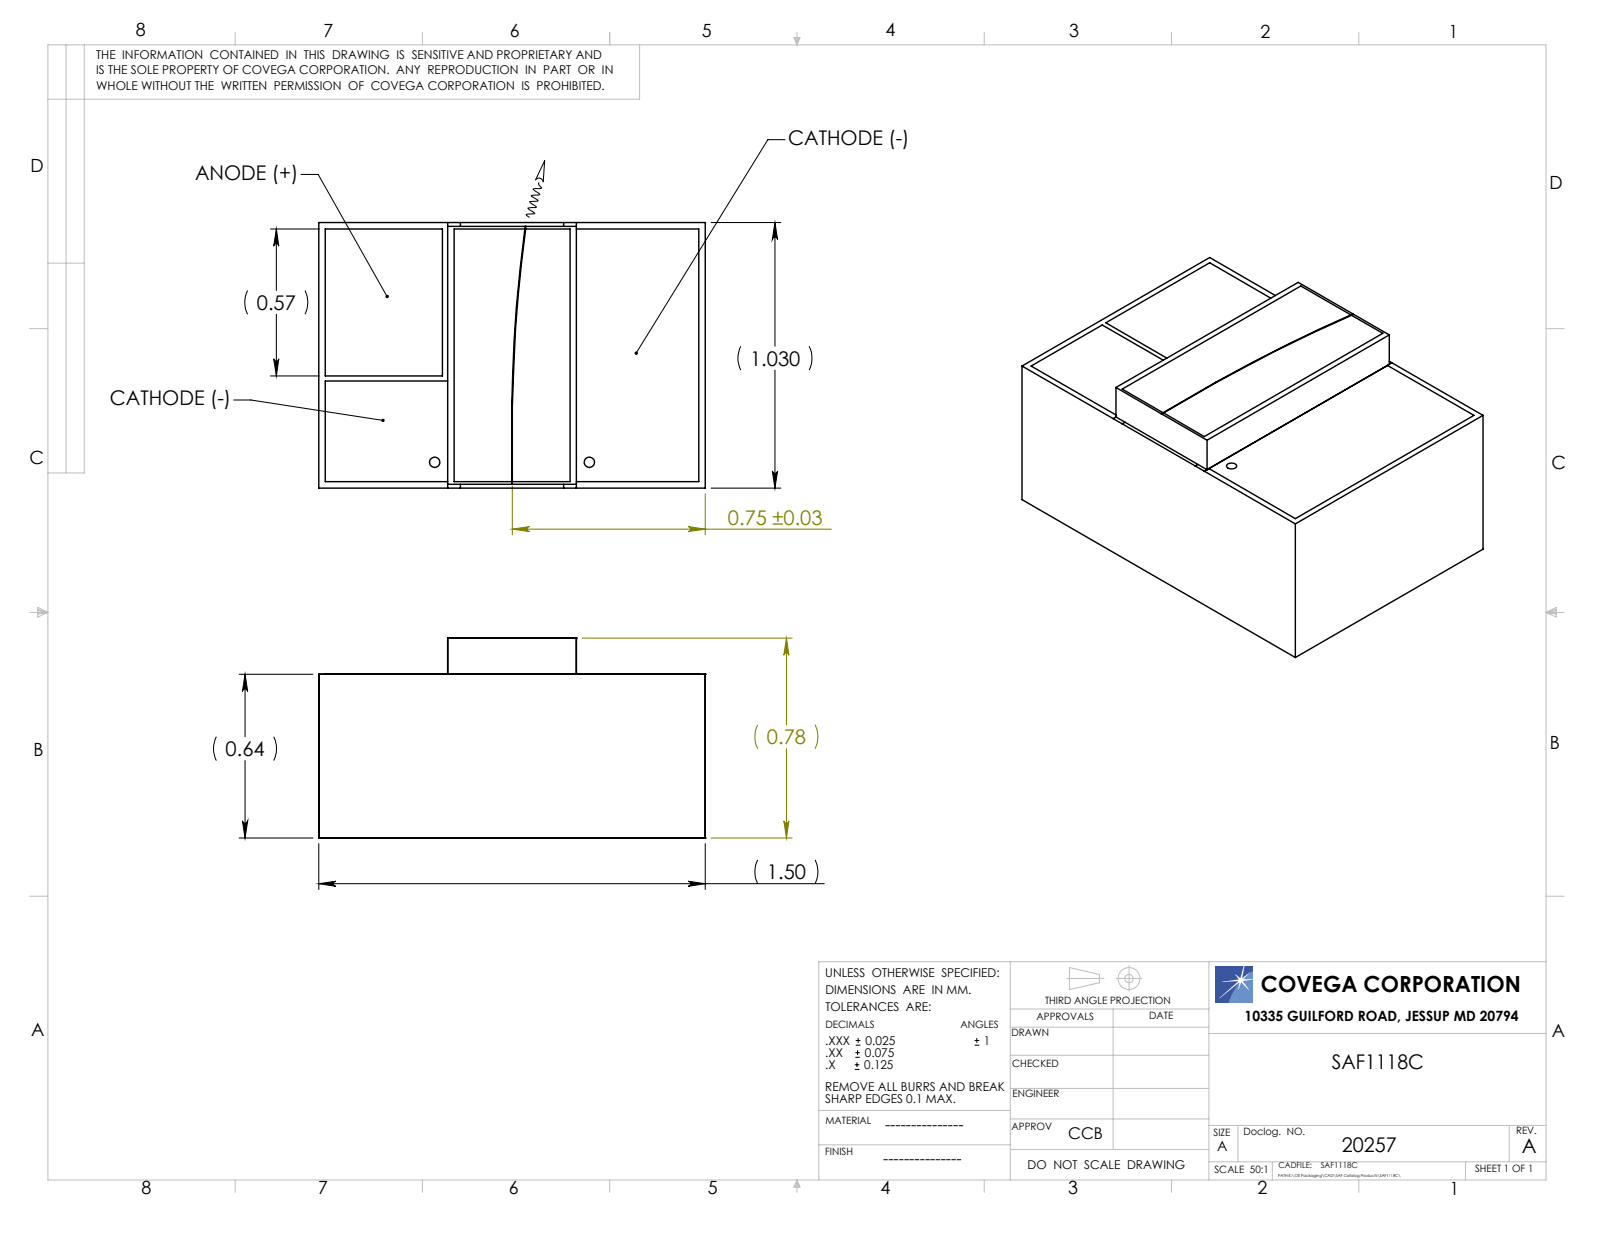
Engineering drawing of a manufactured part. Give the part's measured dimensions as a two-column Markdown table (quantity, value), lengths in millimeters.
| quantity | value |
| --- | --- |
| part name | 20257; 32068-000; 31002-XXX |
| STEP written by | SolidWorks 2009 (AUTOMOTIVE_DESIGN) |
| units | millimeters |
| bodies | 2 solids, 26 faces (26 planar, 0 cylindrical, 0 other) |
| overall size | 1.5 × 1.03 × 0.78 |
| volume | 1 mm³ |
| surface area | 8 mm² |
| main face-to-face distances | 0.64, 1.03, 1.5, 0.78, 0.5, 1, 1.01, 0.99 |
